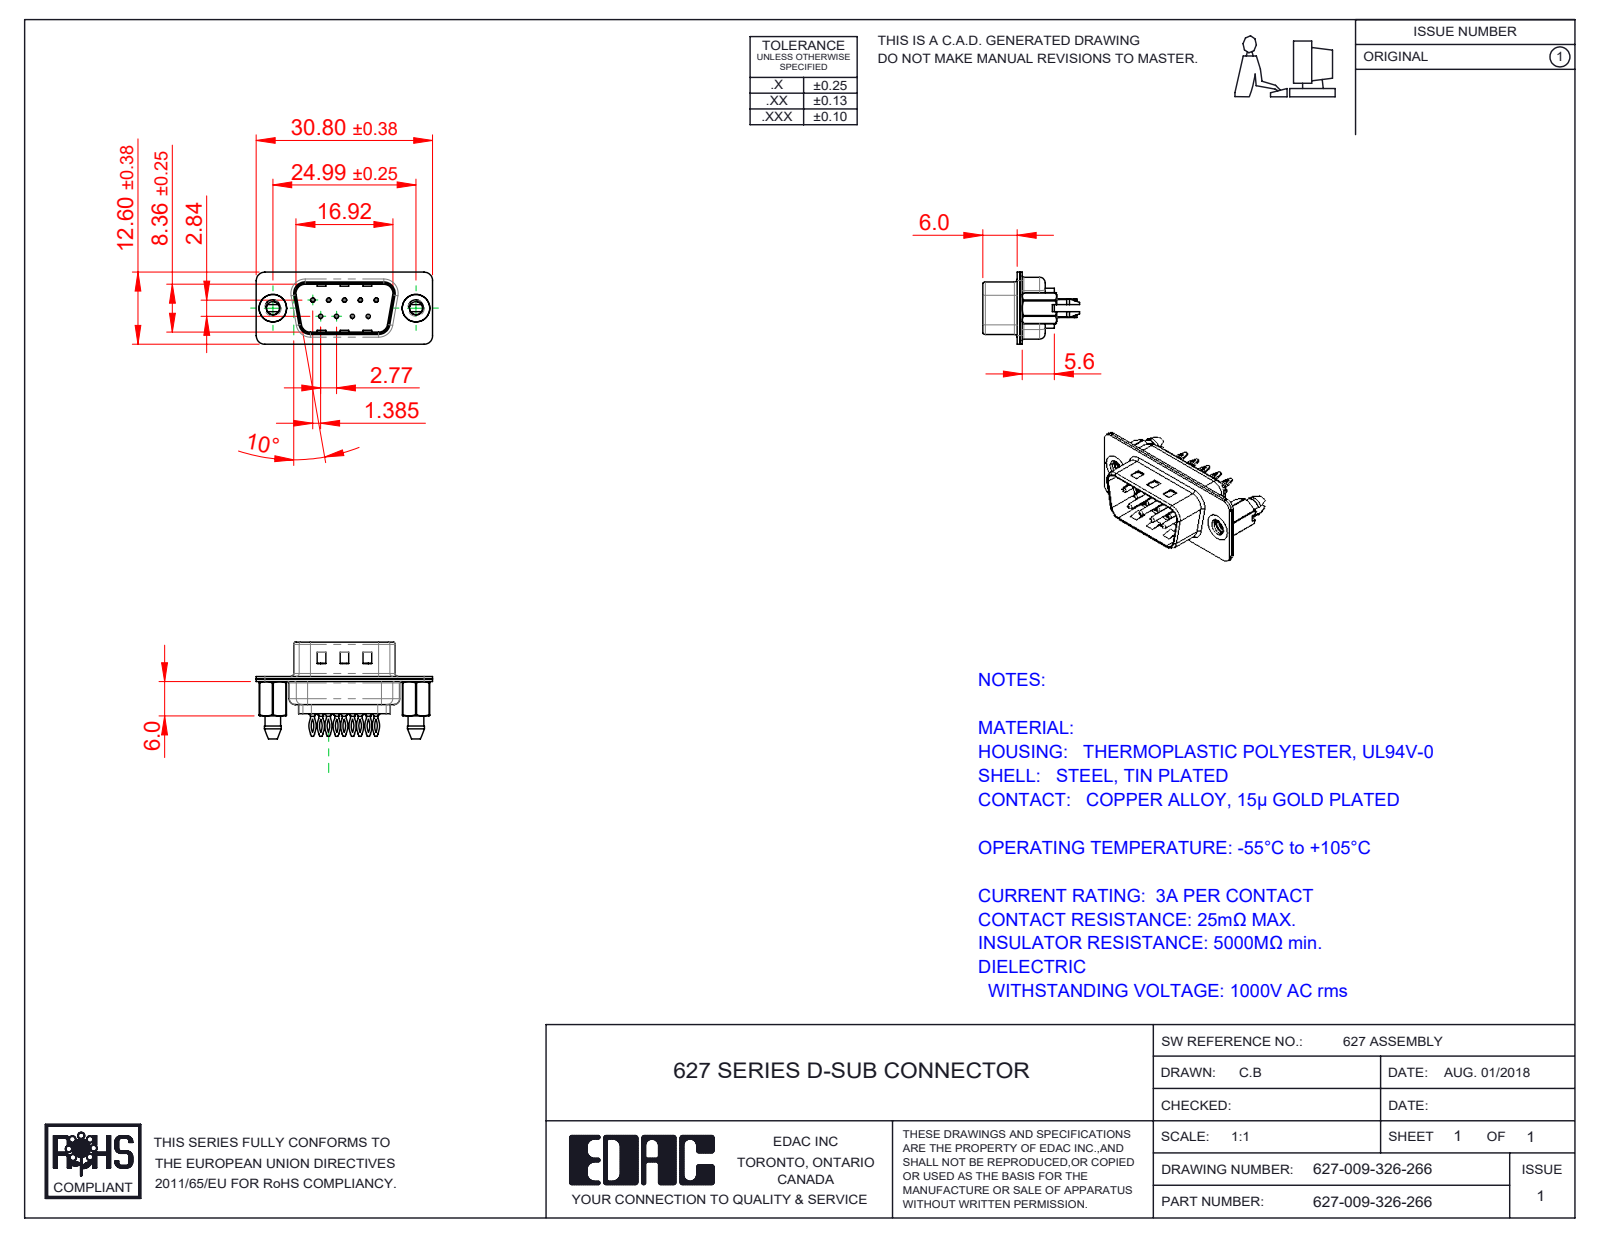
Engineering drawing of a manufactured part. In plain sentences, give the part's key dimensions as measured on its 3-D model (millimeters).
The part is named "627 Shell Rear_09 Contacts; 627 Contact Row 2_26L; 627-009-326-266; 627 Shell Front_09 Contacts (+3 more)". Its 3-D file was written by "SolidWorks 2020 (CONFIG_CONTROL_DESIGN)". It is 14 solids with 1062 faces: 319 planar, 440 cylindrical and 303 other. Overall it measures 30.8 by 16.9 by 12.6 millimeters. Its volume is 1 427 cubic millimeters and its surface area 4 197 square millimeters. Round holes: 9 of diameter 0.35, 9 of diameter 1.1, 9 of diameter 1.6, 2 of diameter 2.26, 2 of diameter 4, 2 of diameter 4.8. Round bosses or shafts: 9 of diameter 2, 9 of diameter 1.5, 9 of diameter 0.75, 2 of diameter 4.9. Partial cylindrical surfaces (rounded edges, fillets, slot ends): 20 of radius 1.5, 18 of radius 2.92, 18 of radius 3.33, 12 of radius 2, 10 of radius 1.6, 8 of radius 0.5, 4 of radius 0.25, 4 of radius 0.6. The main face-to-face distances are 0.4, 0.45, 0.9, 0.82, 9.58, 1.4, 8.76, 6.5, 0.5, 1.5. The hole center spacings are 3.16, 2.77, 5.54, 5.03, 5.04, 8.31, 7.48, 7.49.
